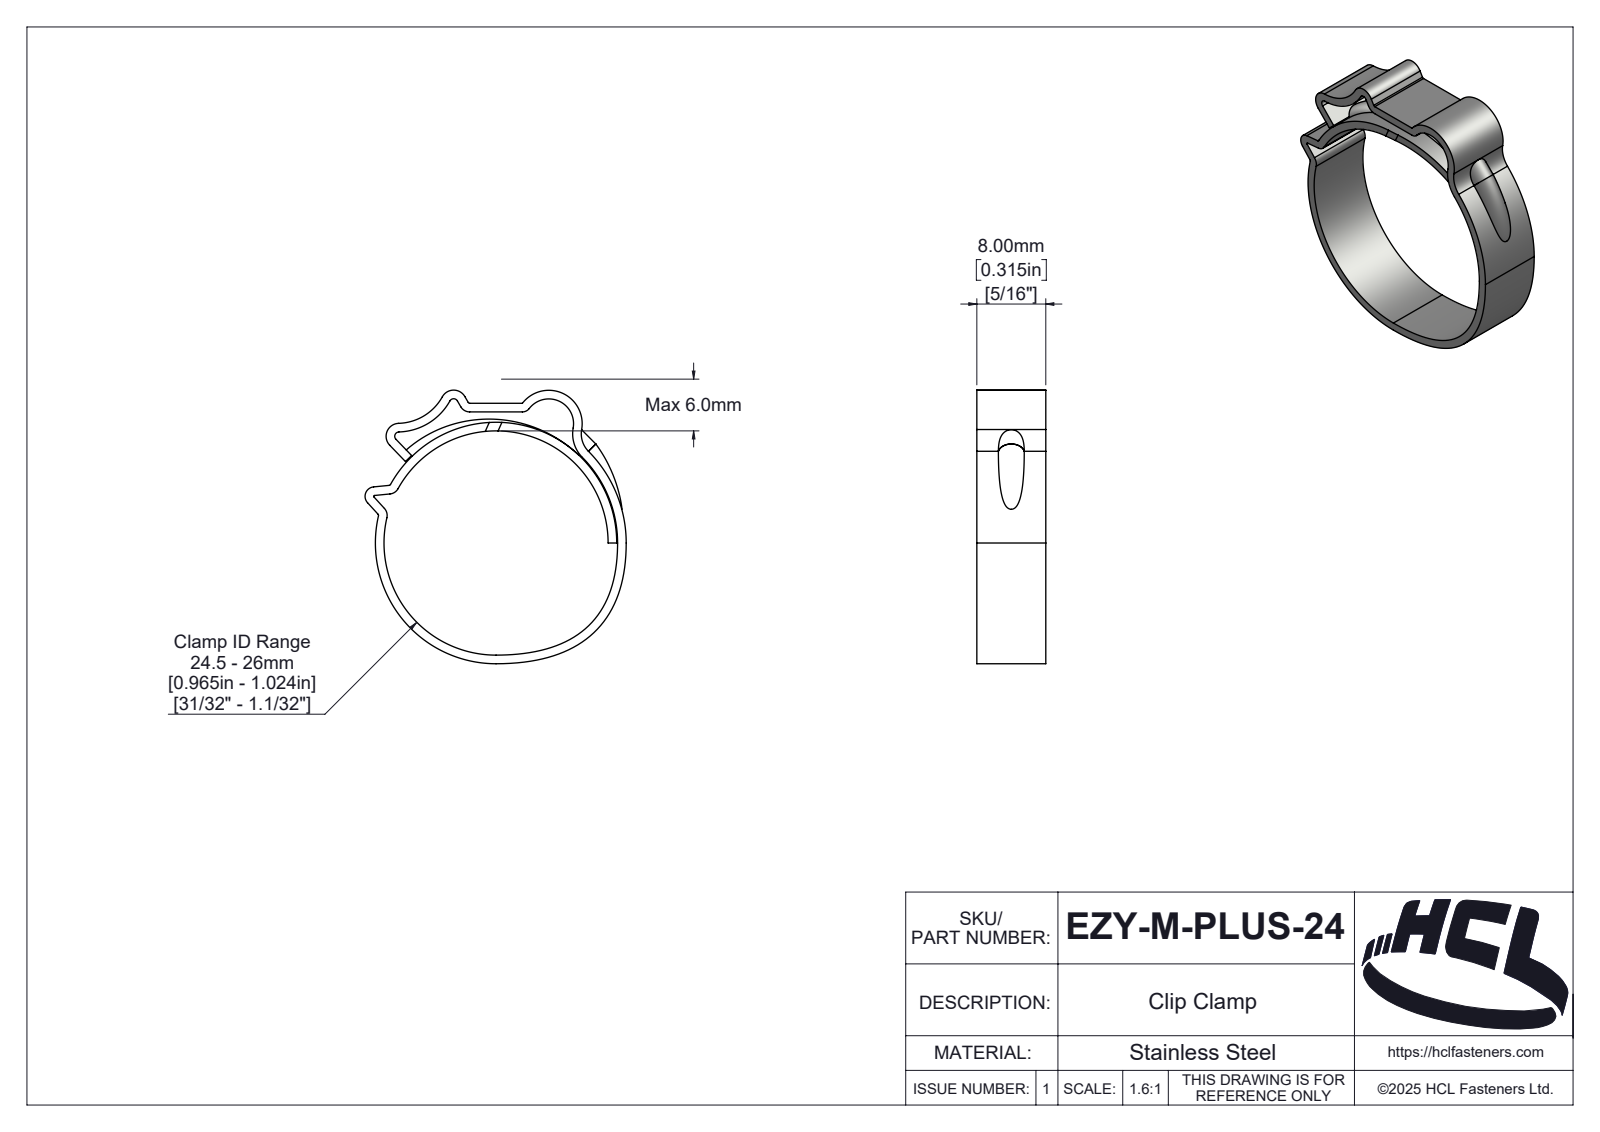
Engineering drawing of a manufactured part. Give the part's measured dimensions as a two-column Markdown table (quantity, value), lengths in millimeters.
| quantity | value |
| --- | --- |
| part name | EZY-M-PLUS-24 |
| STEP written by | SolidWorks 2025 (AUTOMOTIVE_DESIGN) |
| units | millimeters |
| bodies | 2 solids, 170 faces (21 planar, 85 cylindrical, 64 other) |
| overall size | 31.73 × 30.3 × 8 |
| volume | 1 046 mm³ |
| surface area | 2 374 mm² |
| partial cylindrical surfaces (radius × count) | 0.2 × 3, 1.2 × 3, 0.5 × 2, 1.5 × 2, 10 × 2, 0.1 × 1, 0.23 × 1, 0.94 × 1 |
| main face-to-face distances | 8, 1, 15.2, 16.2 |
